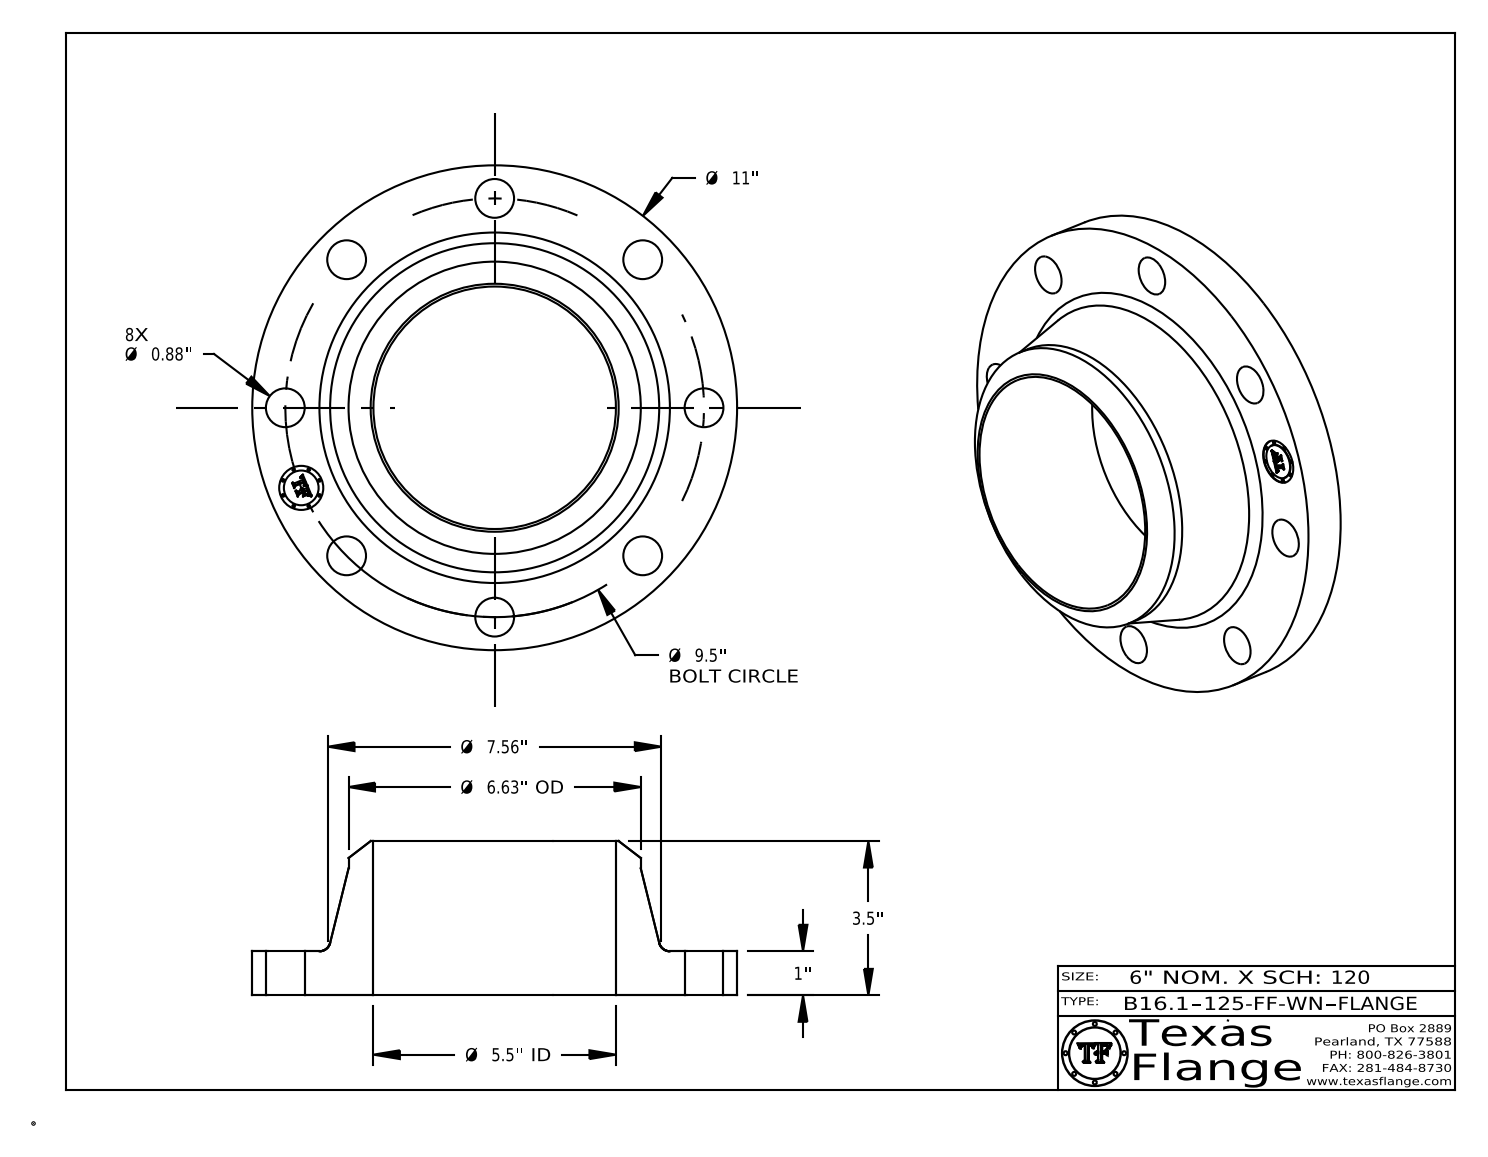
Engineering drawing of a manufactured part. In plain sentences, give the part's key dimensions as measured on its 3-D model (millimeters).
The part is named "B16.1, Class 125-FF-WN". Its 3-D file was written by "CATIA V5 STEP AP214 (AUTOMOTIVE_DESIGN)". It is 1 solid with 416 faces: 368 planar, 42 cylindrical and 6 other. Overall it measures 279.4 by 279.4 by 88.9 millimeters. Its volume is 1 657 000 cubic millimeters and its surface area 186 500 square millimeters. Round holes: 8 of diameter 22.4, 1 of diameter 25.4, 1 of diameter 139.7. Round bosses or shafts: 8 of diameter 1.5, 1 of diameter 279.4, 1 of diameter 168.4, 1 of diameter 20. The main face-to-face distances are 25.4, 88.9, 63.5, 0.4, 25, 63.9, 7.6, 7.4, 1.4, 4.9. The hole center spacings are 120.7, 92.3, 170.6, 222.9, 134.1, 241.3, 241.3, 47.1.
